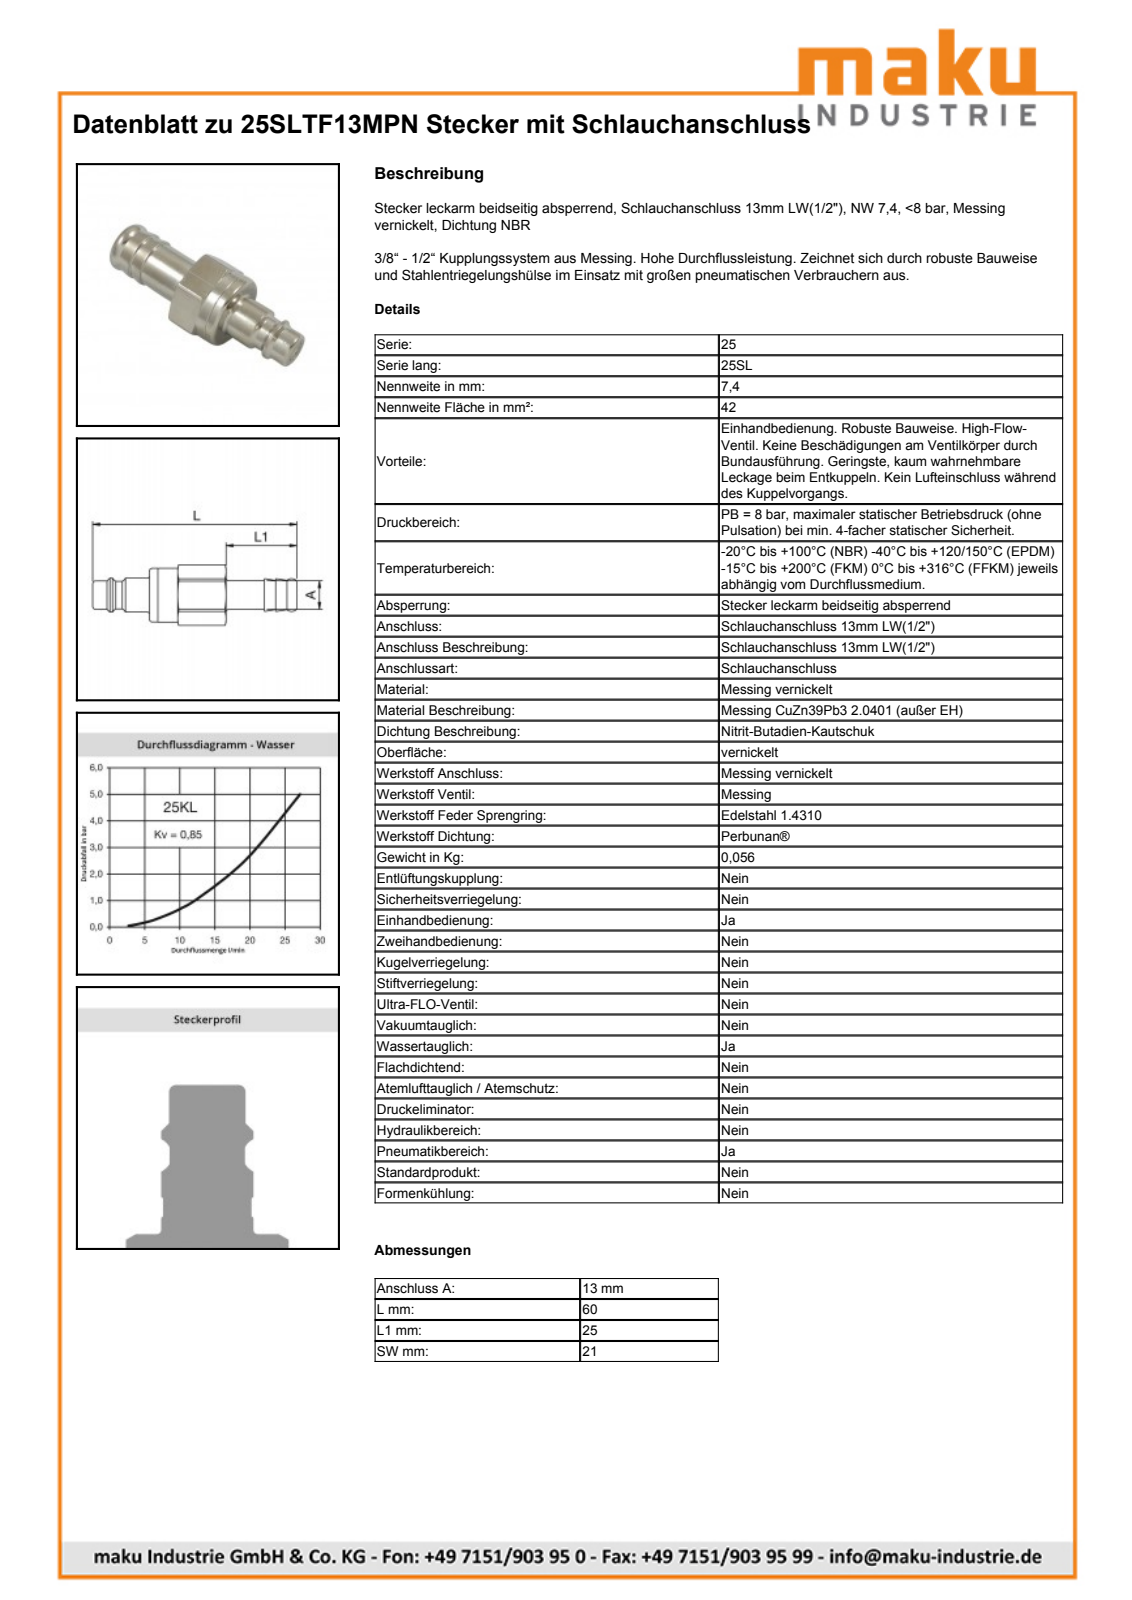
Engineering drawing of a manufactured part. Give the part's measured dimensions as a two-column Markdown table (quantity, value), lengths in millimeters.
| quantity | value |
| --- | --- |
| part name | D113466 |
| STEP written by | Autodesk Inventor 2013 (AUTOMOTIVE_DESIGN) |
| units | millimeters |
| bodies | 1 solid, 58 faces (17 planar, 14 cylindrical, 27 other) |
| overall size | 60 × 23.69 × 21.68 |
| volume | 10 963 mm³ |
| surface area | 3 767 mm² |
| round holes (diameter × count) | 17 × 1 |
| round bosses / shafts (diameter × count) | 21 × 1, 16.5 × 1, 13.1 × 1, 12 × 1, 10 × 1, 9.75 × 1 |
| partial cylindrical surfaces (radius × count) | 11.85 × 1 |
| main face-to-face distances | 21, 15, 40, 25, 20, 35, 60, 23, 3, 12 |
